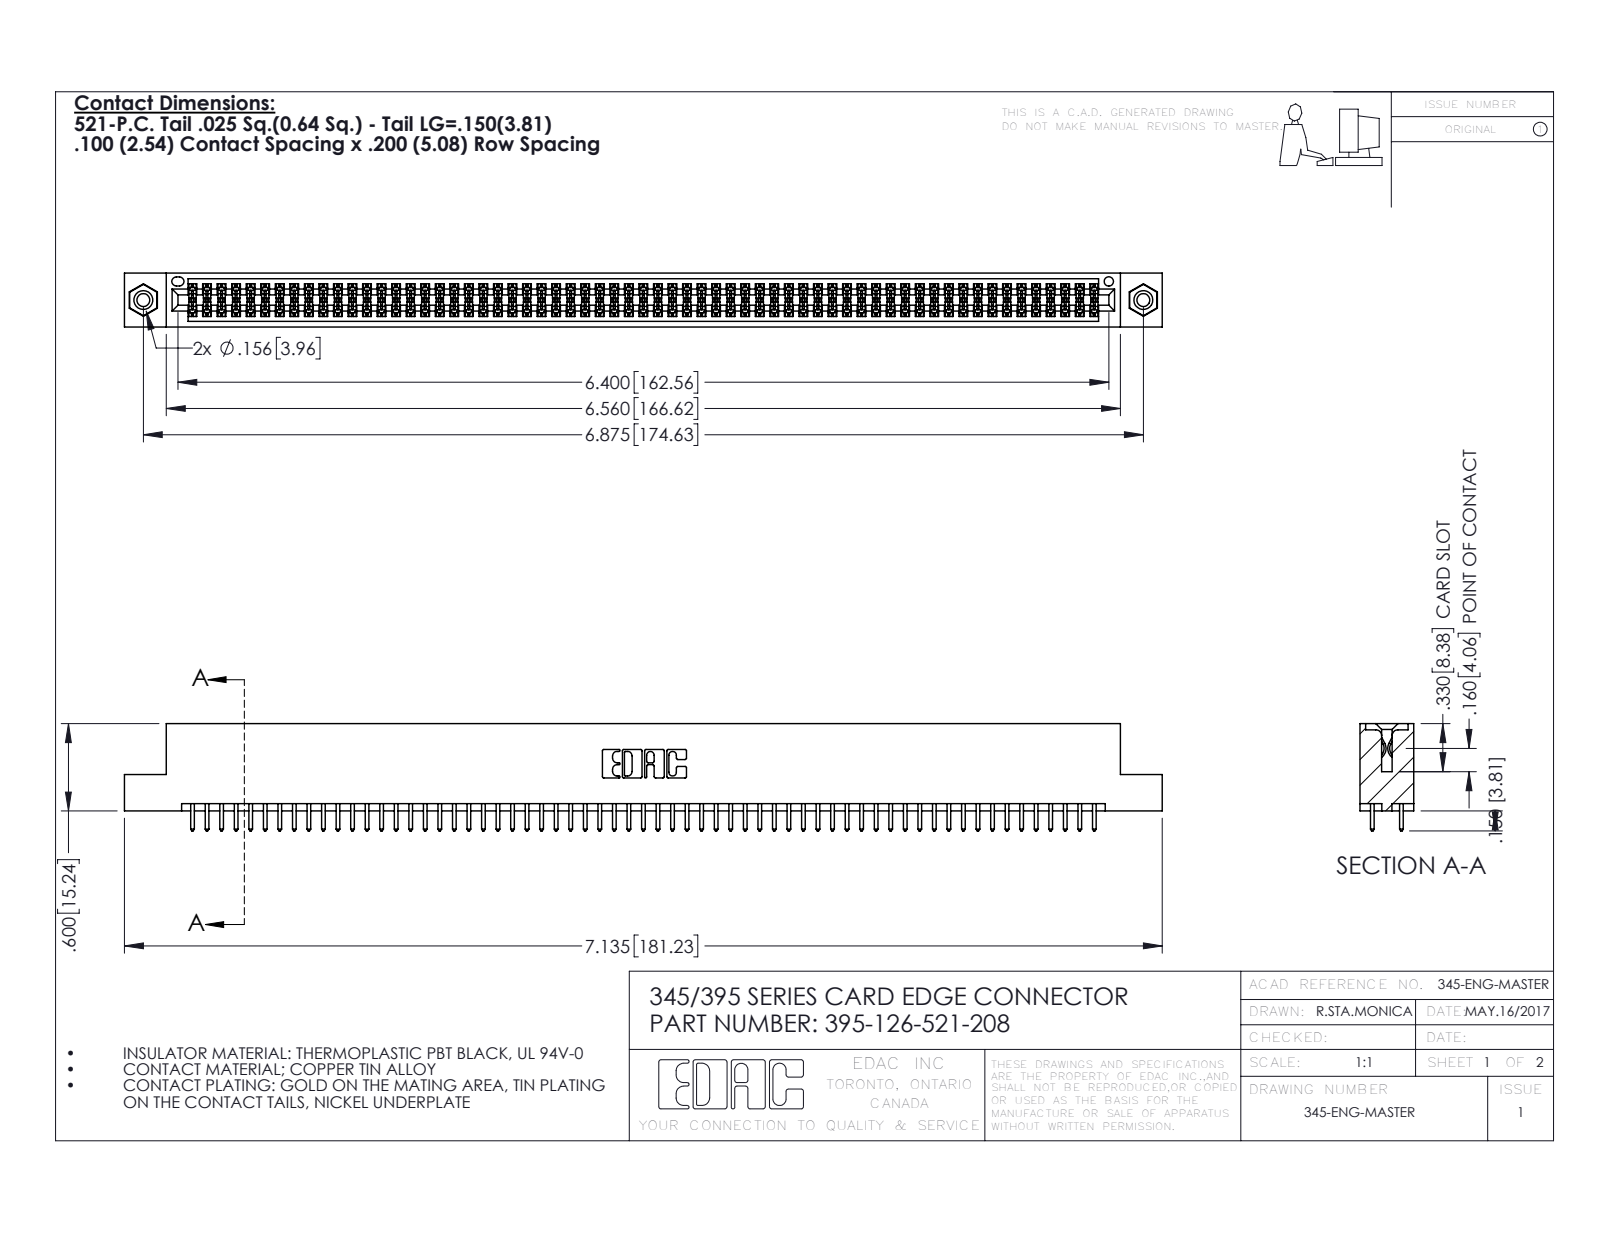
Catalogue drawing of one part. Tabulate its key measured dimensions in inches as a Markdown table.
| quantity | value |
| --- | --- |
| part name | 345-250-001_345-250-003-102; 345 Part_Flush Mounting Lugs - 0.156 Dia-TI; 395-126-521-208; 345-292-001_345-293-121 |
| STEP written by | SolidWorks 2016 (CONFIG_CONTROL_DESIGN) |
| units | inches |
| bodies | 129 solids, 6486 faces (4270 planar, 2200 cylindrical, 16 other) |
| overall size | 7.135 × 0.737 × 0.37 |
| volume | 1.083 in³ |
| surface area | 40.78 in² |
| round holes (diameter × count) | 0.089 × 2, 0.125 × 2, 0.156 × 2, 0.064 × 1 |
| round bosses / shafts (diameter × count) | 0.155 × 2 |
| partial cylindrical surfaces (radius × count) | 0.006 × 189, 0.01 × 126, 0.01 × 22, 0.007 × 6, 0.031 × 6, 0.026 × 3, 0.014 × 2, 0.019 × 2 |
| main face-to-face distances | 0.072, 0.298, 0.2, 0.098, 0.272, 0.025, 0.37, 0.225, 0.175, 0.149 |
| hole center spacings | 0.27, 6.639, 6.875 |
